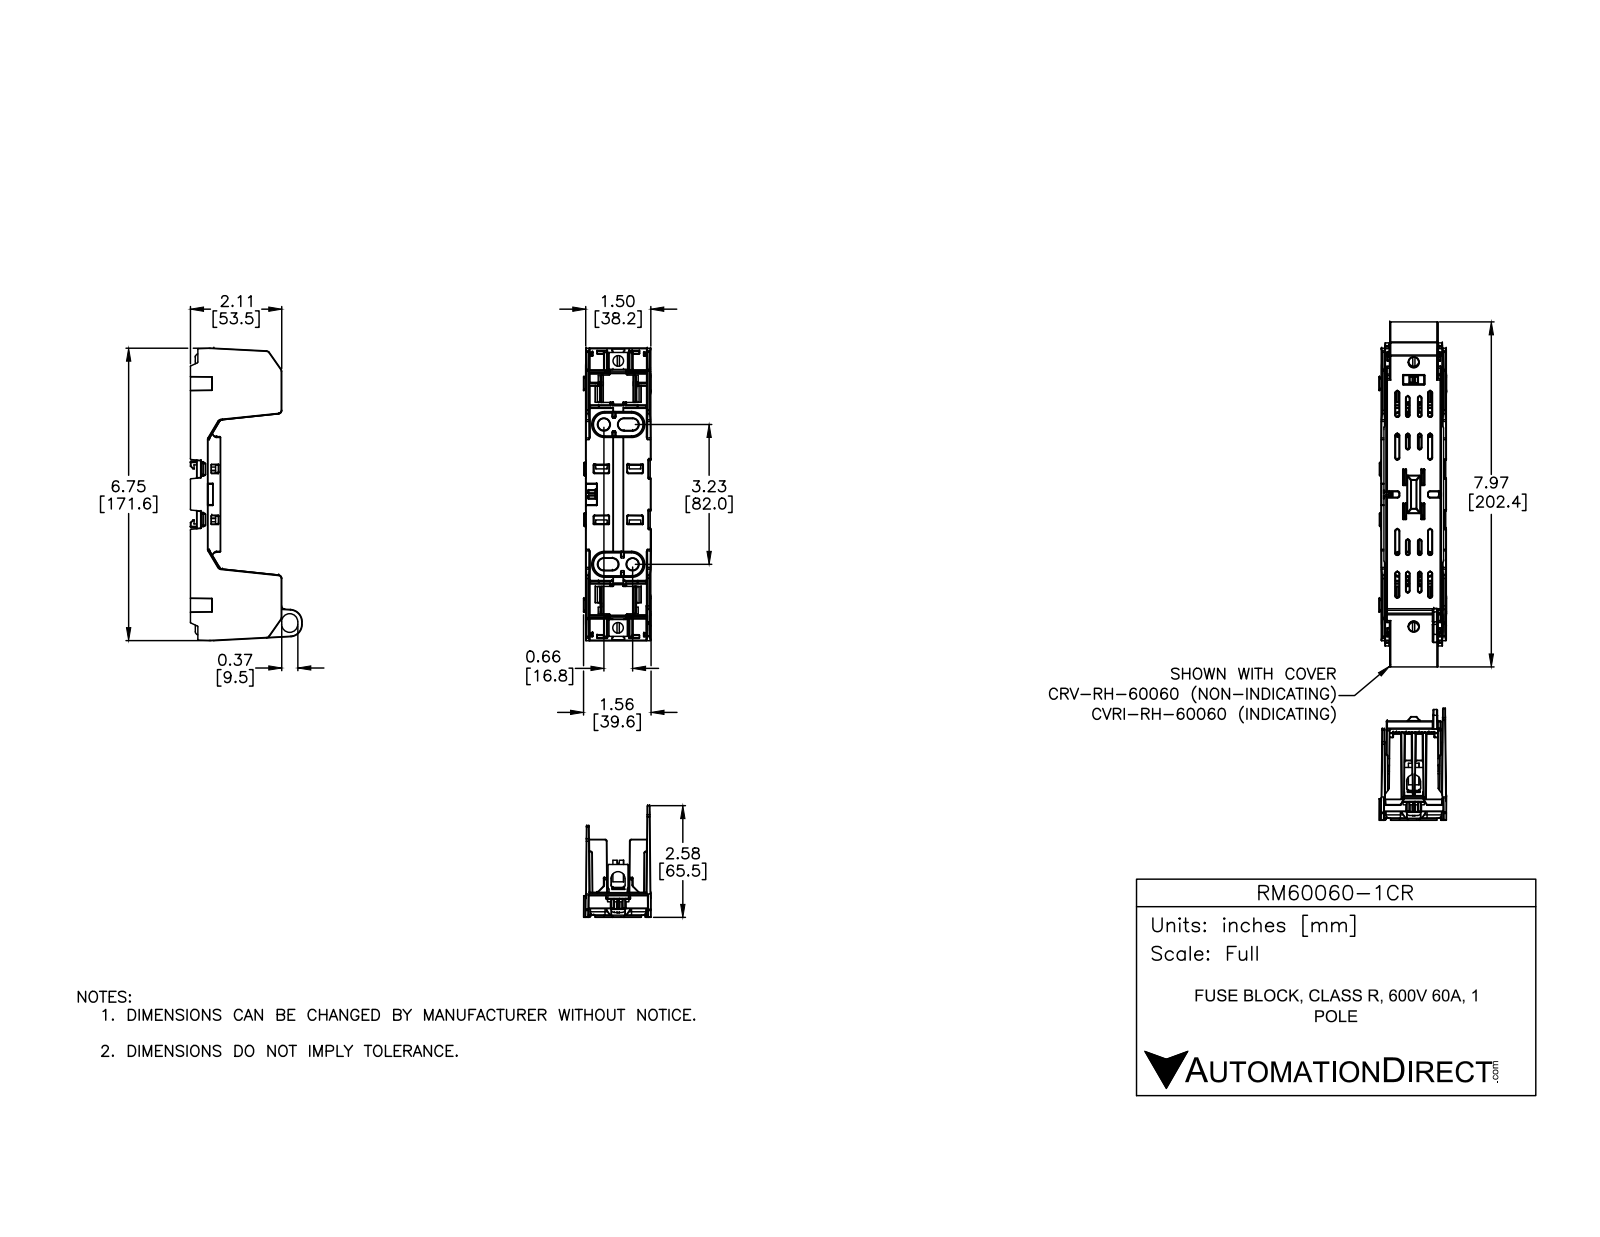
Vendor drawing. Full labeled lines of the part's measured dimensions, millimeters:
Part name (STEP PRODUCT): RM60060-1CR
STEP written by: SolidWorks 2021 (CONFIG_CONTROL_DESIGN)
Units: millimetres
Bodies: 7 solids, 797 faces (467 planar, 219 cylindrical, 111 other)
Overall size (bounding box): 171.6 × 65.5 × 39.6
Volume: 84 230 mm³ · Surface area: 49 670 mm²
Round holes (diameter × count): ⌀6.2 ×2, ⌀7.1 ×2
Round bosses / shafts (diameter × count): ⌀8.5 ×2, ⌀6.2 ×2
Partial cylindrical surfaces — rounded edges, fillets, slot ends (radius × count): R0.2 ×35, R0.3 ×22, R0.5 ×16, R1 ×8, R0.3 ×4, R0.9 ×4, R1.8 ×4, R2 ×4
Main face-to-face distances: 38.3, 5.1, 14.5, 9.4, 2, 143.7, 8.5, 3.4, 6, 0.7
Hole centre spacings: 38.3, 119.6, 83.7, 156.6
